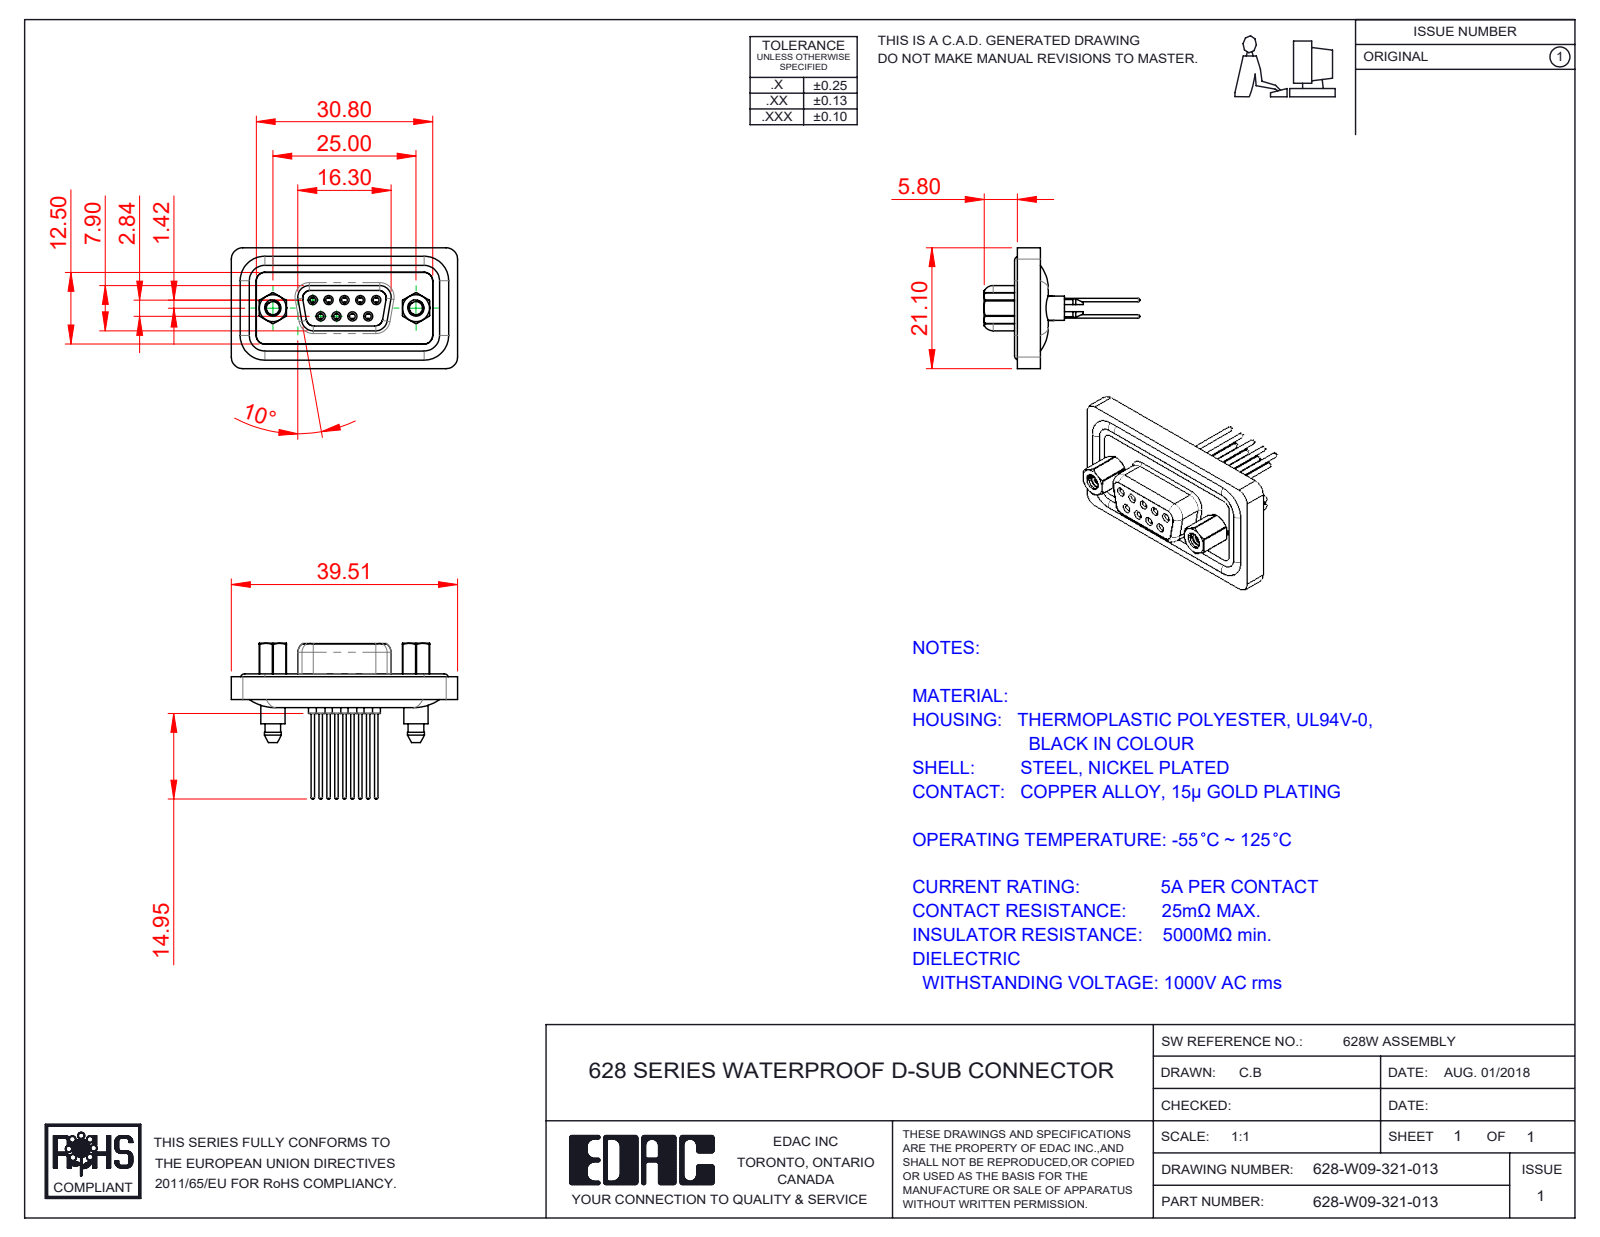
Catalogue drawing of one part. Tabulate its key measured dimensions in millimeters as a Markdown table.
| quantity | value |
| --- | --- |
| part name | 628W Shell Front_09 Contacts; 628W Housing_09 Contacts; 628W Contact Row 2_21; 628W Waterproof Housing_09 Contacts BL (+4 more) |
| STEP written by | SolidWorks 2020 (CONFIG_CONTROL_DESIGN) |
| units | millimeters |
| bodies | 17 solids, 982 faces (250 planar, 437 cylindrical, 295 other) |
| overall size | 39.51 × 27.2 × 21.1 |
| volume | 4 522 mm³ |
| surface area | 7 709 mm² |
| round holes (diameter × count) | 1 × 9, 1.1 × 9, 1.5 × 9, 1.7 × 9, 1.8 × 9, 2 × 9, 2.26 × 2, 2.29 × 2, 4 × 2, 4.25 × 2, 4.8 × 2 |
| round bosses / shafts (diameter × count) | 1.6 × 13, 2.2 × 9, 0.6 × 9, 1.5 × 4, 5.4 × 2, 4.9 × 2, 2.79 × 2, 4.8 × 1 |
| partial cylindrical surfaces (radius × count) | 1.5 × 16, 2 × 14, 1.35 × 8, 1.6 × 6, 0.5 × 4, 0.9 × 4, 1.75 × 4, 2.7 × 4 |
| main face-to-face distances | 0.4, 1.6, 2.9, 1.1, 1.8, 2.5, 3.6, 4, 0.7, 0.5 |
| hole center spacings | 3.16, 2.77, 5.54, 5.03, 5.04, 7.48, 7.49, 8.31 |
